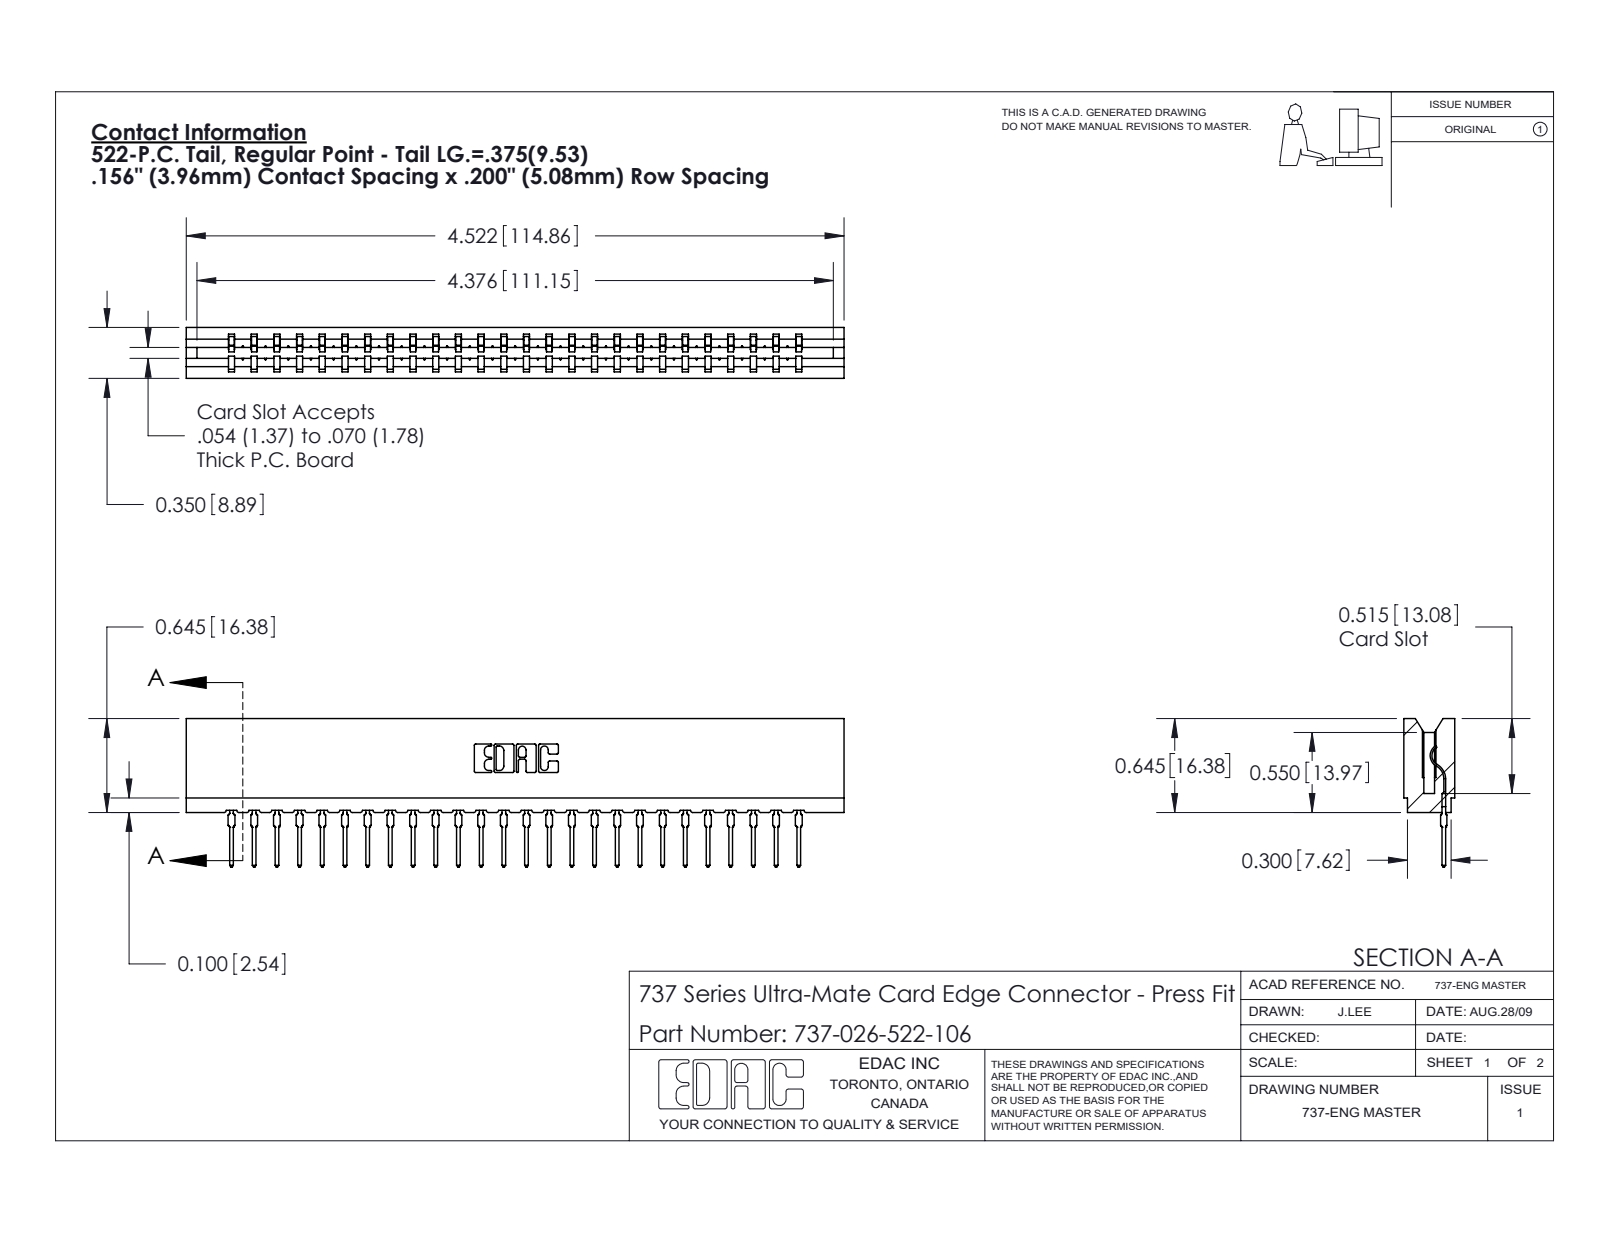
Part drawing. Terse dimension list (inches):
name: 745-292-001_522; 737-026-522-106; 737 Part_Insulator Option - 06
written by: SolidWorks 2020 (CONFIG_CONTROL_DESIGN)
unit: in
bodies: 27 solids, 3033 faces (1823 planar, 534 cylindrical, 676 other)
size: 4.522 × 1.021 × 0.35
volume: 0.684 in³; area: 23 in²
rounds: 52× R0.015, 52× R0.021, 22× R0.01, 6× R0.007, 6× R0.031, 4× R0.005, 4× R0.011, 3× R0.026
face distances: 0.138, 0.212, 0.35, 0.624, 0.074, 0.156, 0.045, 0.305, 0.093, 0.167
